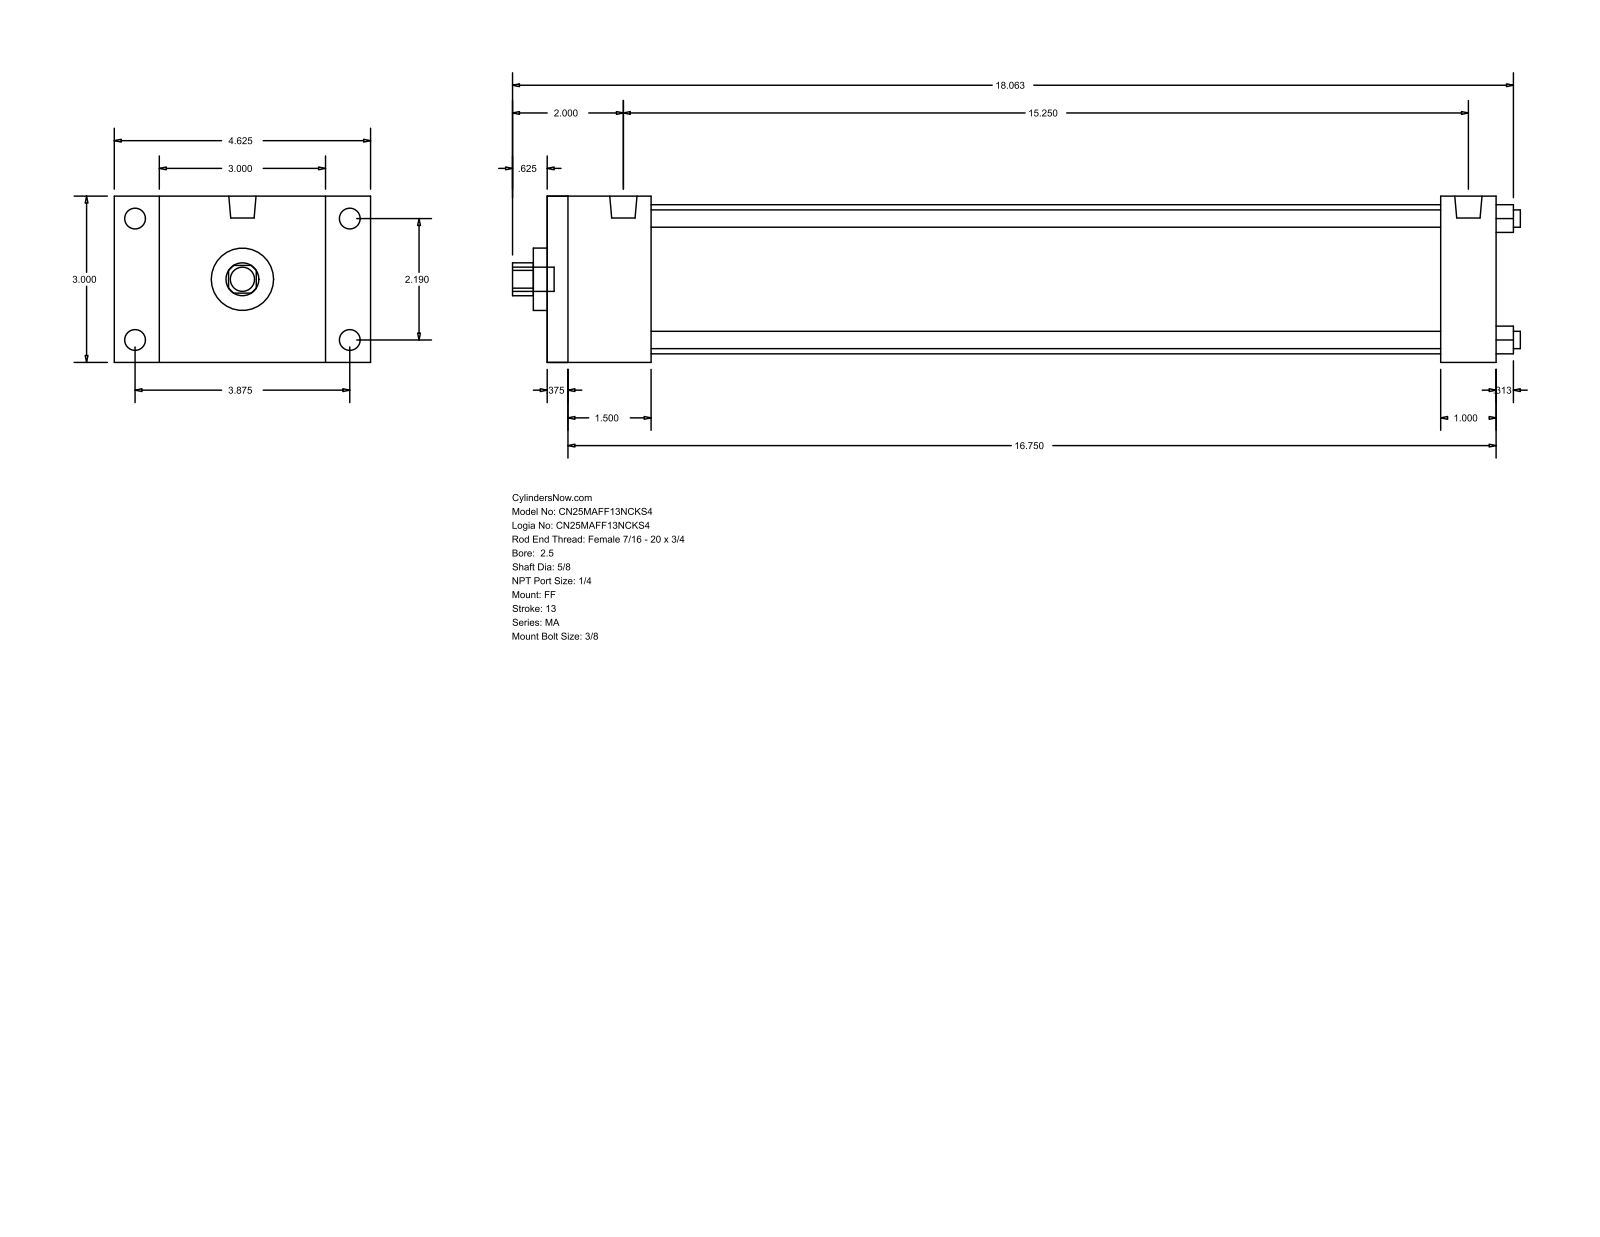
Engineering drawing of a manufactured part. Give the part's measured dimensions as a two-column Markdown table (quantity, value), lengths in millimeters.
| quantity | value |
| --- | --- |
| part name | MA_FF__0250_0.625 |
| STEP written by | GSSL Pune (CONFIG_CONTROL_DESIGN) |
| units | millimeters |
| bodies | 0 solids, 92 faces (64 planar, 28 cylindrical, 0 other) |
| overall size | 461.96 × 117.47 × 76.2 |
| round holes (diameter × count) | 7.94 × 4, 15.88 × 1, 28.57 × 1, 68.33 × 1 |
| round bosses / shafts (diameter × count) | 9.53 × 4, 7.94 × 4, 12.49 × 2, 11.11 × 1 |
| partial cylindrical surfaces (radius × count) | 7.54 × 1 |
| main face-to-face distances | 76.2, 434.97, 9.52, 425.45, 25.4, 47.62, 409.57, 38.1, 400.05, 361.95 |
| hole center spacings | 39.33, 55.62, 78.66 |
